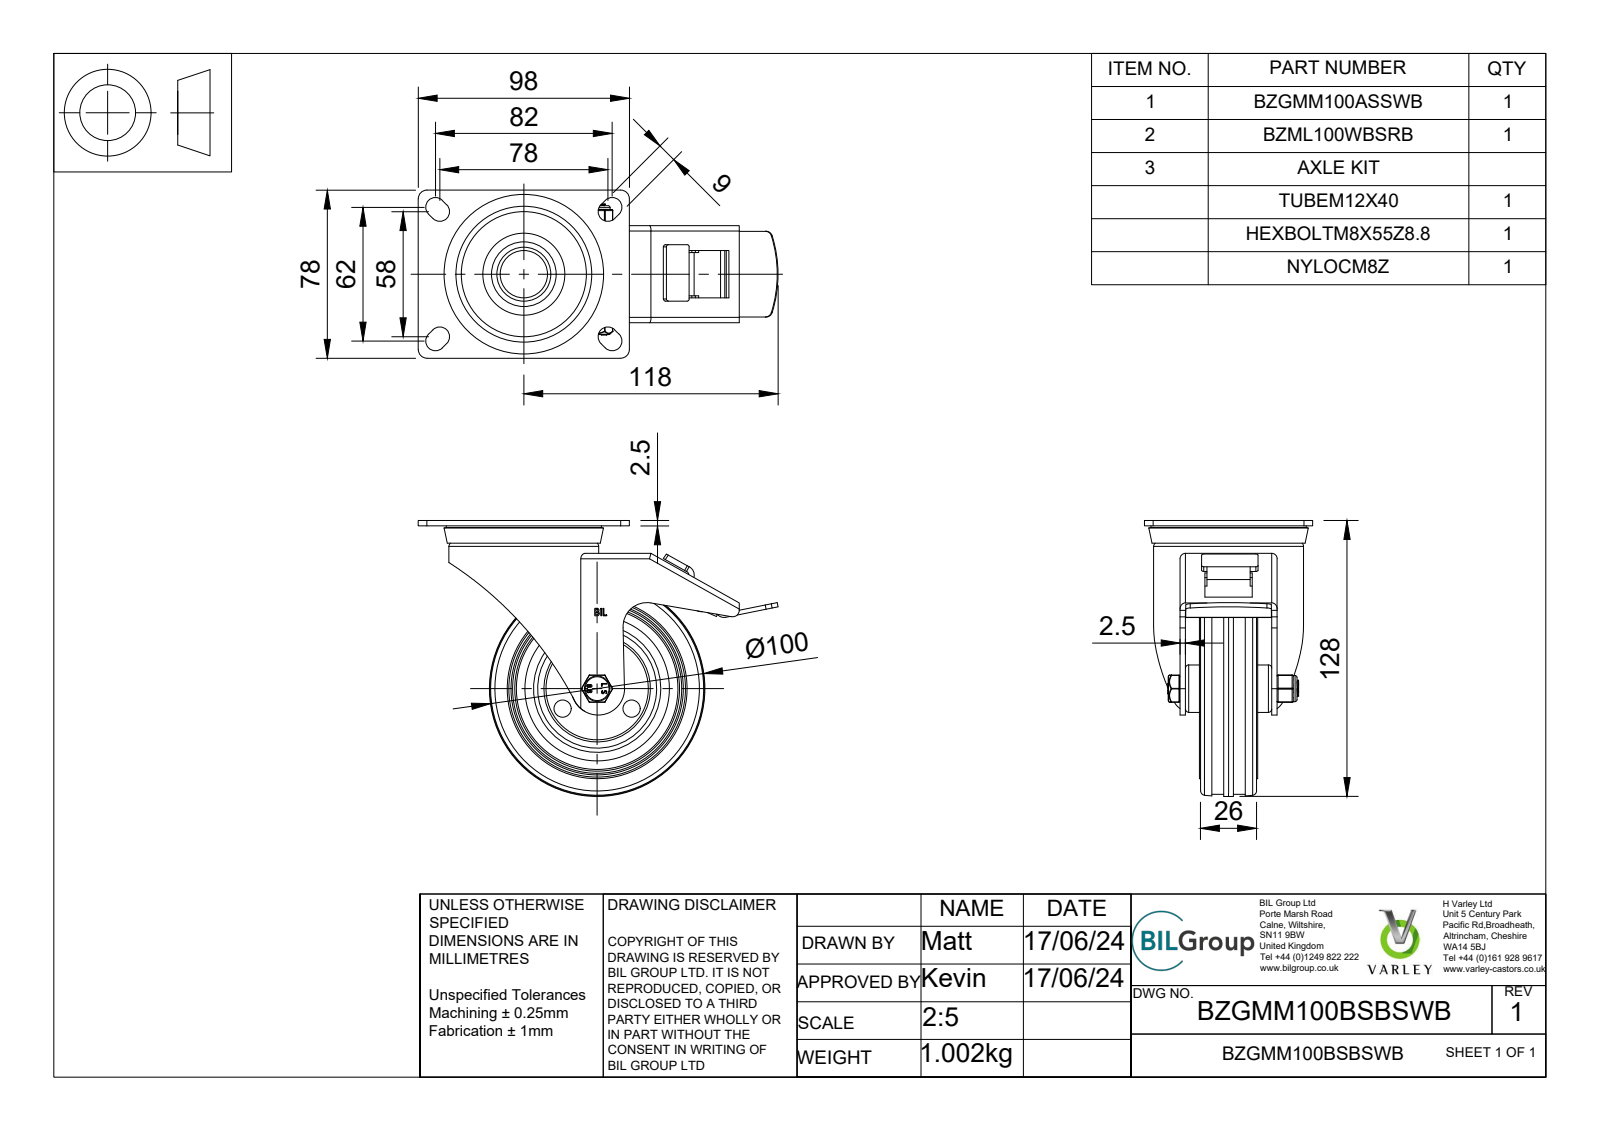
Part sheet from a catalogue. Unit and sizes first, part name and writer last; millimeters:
Units: millimetres
Overall size (bounding box): 167 × 128 × 78
Round holes (diameter × count): ⌀5 ×3, ⌀0.66 ×2, ⌀8 ×1, ⌀8.2 ×1, ⌀8.4 ×1, ⌀8.6 ×1, ⌀12.2 ×1, ⌀12.5 ×1, ⌀20 ×1, ⌀26 ×1, ⌀30 ×1, ⌀50.93 ×1
Round bosses / shafts (diameter × count): ⌀3.5 ×8, ⌀8 ×3, ⌀100 ×1, ⌀98 ×1, ⌀83.5 ×1, ⌀80 ×1, ⌀76.5 ×1, ⌀69.5 ×1
Partial cylindrical surfaces — rounded edges, fillets, slot ends (radius × count): R0.5 ×18, R0.25 ×12, R1.25 ×8, R4.5 ×8, R4 ×5, R0.33 ×4, R0.64 ×4, R1 ×4
Main face-to-face distances: 2.5, 0.5, 26, 10, 1, 7.5, 7, 33, 9.5, 35.5
Hole centre spacings: 18.5, 32.04, 3.22, 2.49, 15.31, 16.75, 17.5, 19.96
Volume: 254 907 mm³ · Surface area: 132 150 mm²
Bodies: 51 solids, 644 faces (288 planar, 217 cylindrical, 139 other)
Part name (STEP PRODUCT): BZGMM100BSBSWB v3; BZGMM100ASSWB - 2 v1; ZINC PLATED, PRESSED STEEL FORKS; BRAKE PAD (+7 more)
STEP written by: Autodesk Translation Framework v13.14.0.145 (AUTOMOTIVE_DESIGN)
